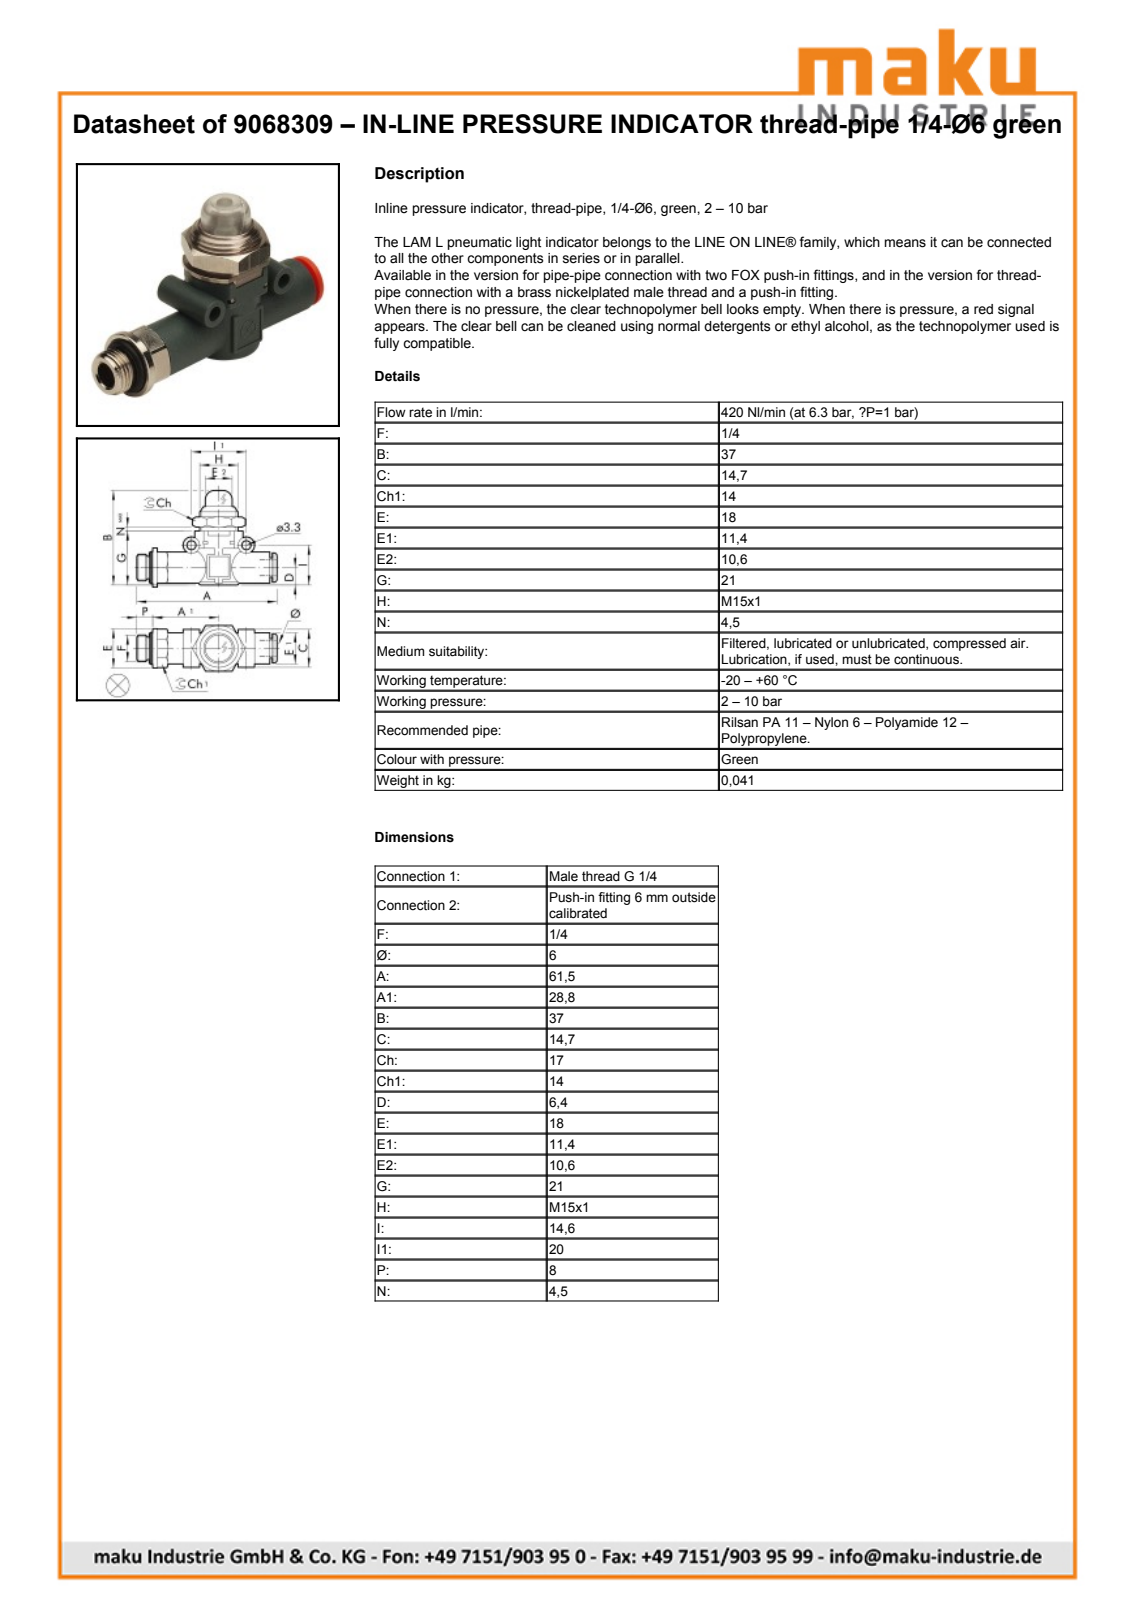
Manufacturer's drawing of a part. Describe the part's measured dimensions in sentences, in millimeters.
The part is named "9068309; LINE-ON-LINE D6 V2v/V3V_L body; LINE-ON-LINE D6 VNR-L bushing; LINE-ON-LINE D6-1/4 thread port (+1 more)". Its 3-D file was written by "PARTsolutions (AUTOMOTIVE_DESIGN)". It is 4 solids with 190 faces: 97 planar, 63 cylindrical and 30 other. Overall it measures 61.5 by 39.6 by 18 millimeters. Its volume is 8 802 cubic millimeters and its surface area 8 131 square millimeters. Round holes: 2 of diameter 3.3, 1 of diameter 3.5, 1 of diameter 4, 1 of diameter 6, 1 of diameter 6.2, 1 of diameter 8, 1 of diameter 9, 1 of diameter 9.6, 1 of diameter 10.3, 1 of diameter 11.6. Round bosses or shafts: 2 of diameter 6, 1 of diameter 18, 1 of diameter 14.8, 1 of diameter 14, 1 of diameter 13.16, 1 of diameter 11.4, 1 of diameter 11.1, 1 of diameter 11. Partial cylindrical surfaces (rounded edges, fillets, slot ends): 2 of radius 7.95, 1 of radius 3.75, 1 of radius 7.5, 1 of radius 7.9, 1 of radius 9.1, 1 of radius 9.15, 1 of radius 9.65. The main face-to-face distances are 14, 17, 14.25, 2.8, 2, 18.4, 12.1, 9.8, 9.3, 16.75. The hole center spacings are 12.74, 20.
